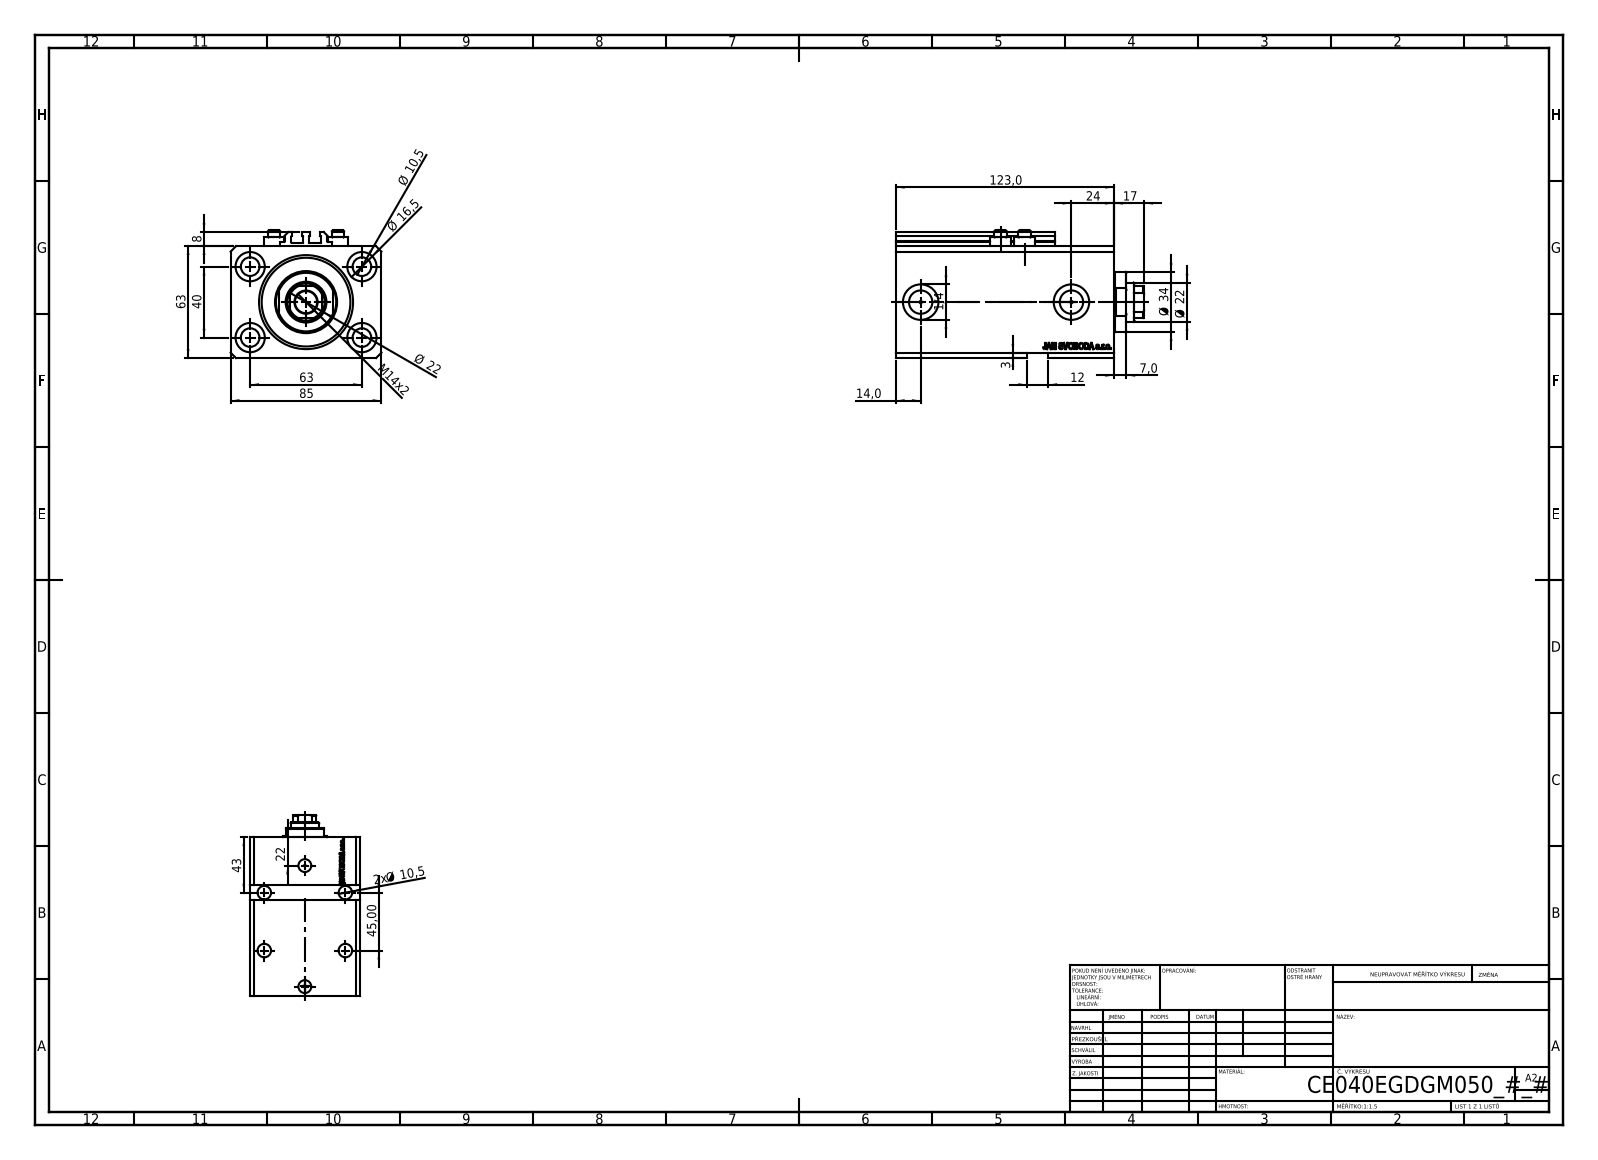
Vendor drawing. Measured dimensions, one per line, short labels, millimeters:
name: ALLEN BOLT V250CE; V250CE_VC_E; V250CE_C_VCP; V250CE_E_Body
written by: SolidWorks 2019 (CONFIG_CONTROL_DESIGN)
unit: mm
bodies: 8 solids, 1123 faces (539 planar, 158 cylindrical, 426 other)
size: 140 × 85 × 72
volume: 553 016 mm³; area: 120 484 mm²
holes: 8× ⌀10.5, 4× ⌀1.25, 4× ⌀4, 4× ⌀16.5, 2× ⌀10, 2× ⌀13.16, 2× ⌀20, 1× ⌀12.5, 1× ⌀22, 1× ⌀40, 1× ⌀53
bosses: 4× ⌀11.6, 4× ⌀7, 1× ⌀34
rounds: 10× R0.2, 1× R10.5
face distances: 63, 85, 123, 17, 106, 11.4, 94.6, 111.6, 3, 56
hole spacings: 37.31, 63, 13.6, 15.4, 24.96, 27.54, 33.62, 36
